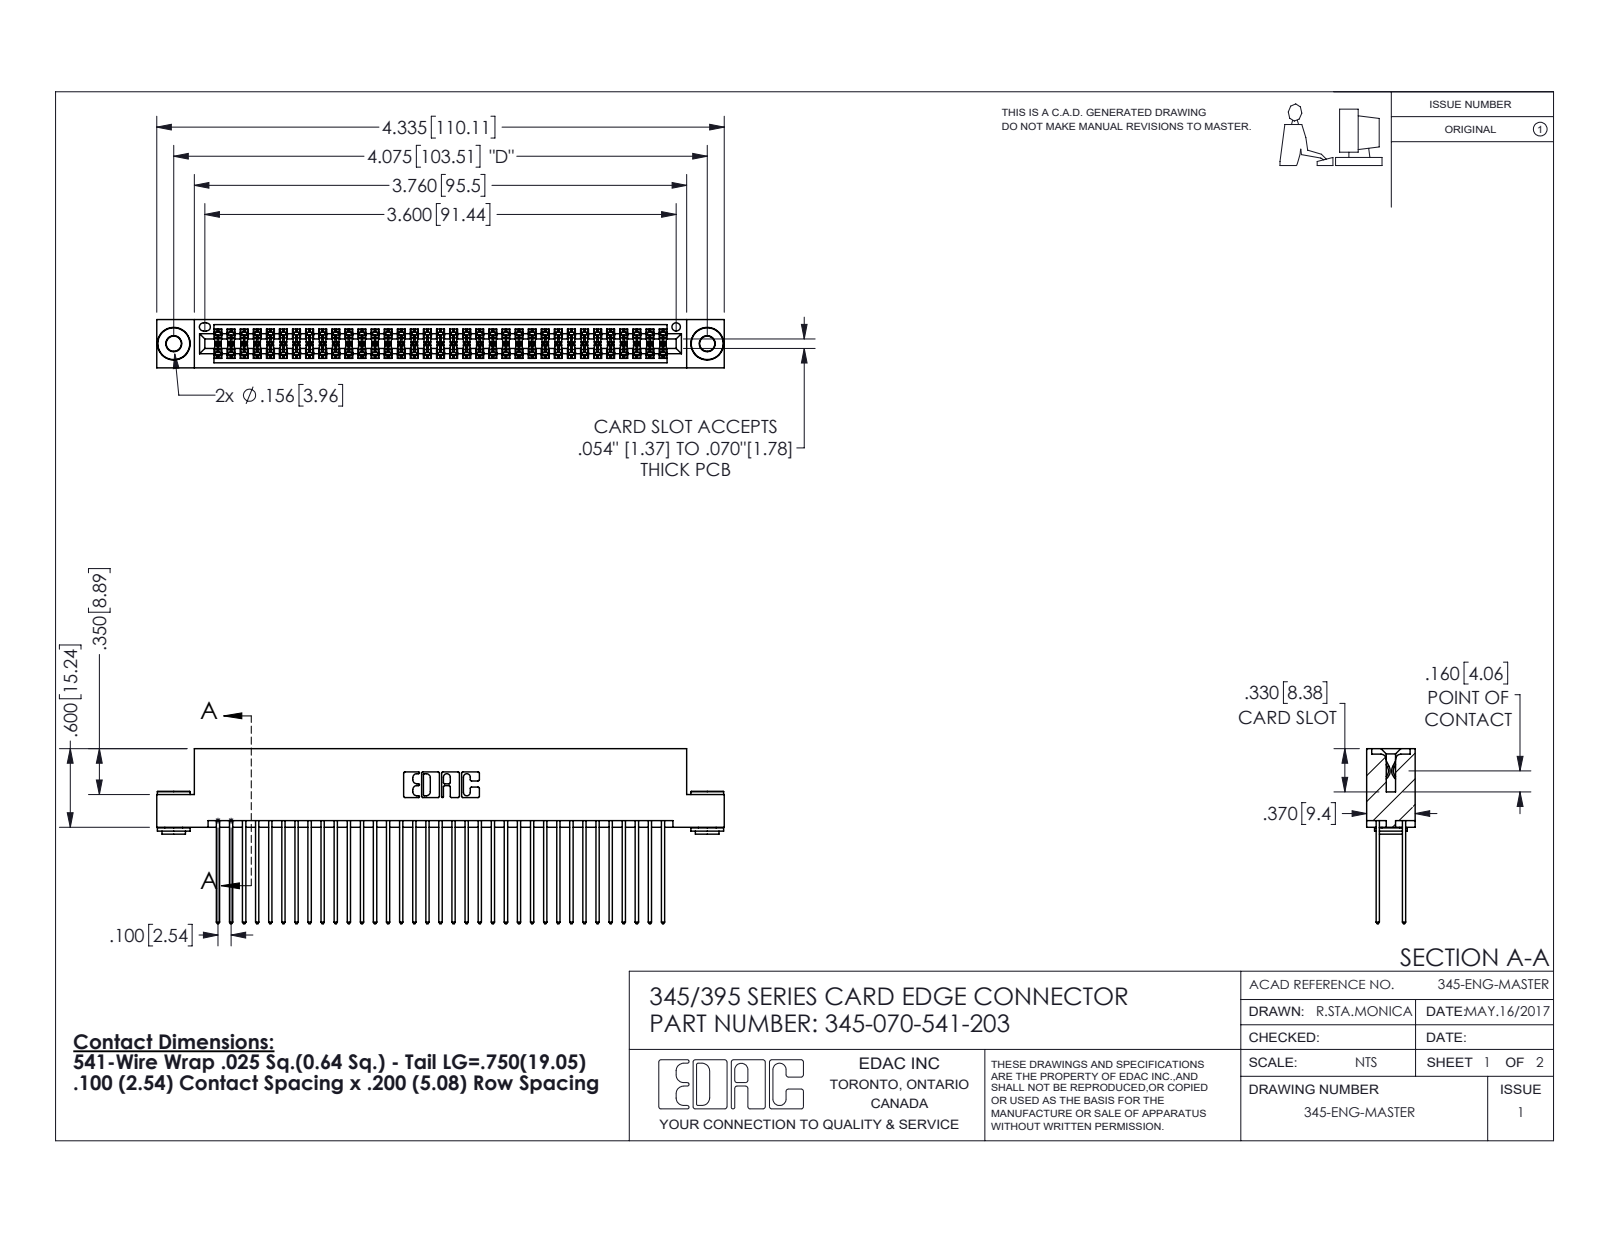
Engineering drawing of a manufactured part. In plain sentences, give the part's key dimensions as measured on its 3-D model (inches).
The part is named "345-070-541-203; 345 Part_Flush Mounting Lugs - 0.156 Dia-TH; 345-292-001_345-293-141; 345-250-002_345-250-002-102". Its 3-D file was written by "SolidWorks 2016 (CONFIG_CONTROL_DESIGN)". It is 73 solids with 3664 faces: 2400 planar, 1256 cylindrical and 8 other. Overall it measures 4.335 by 1.337 by 0.37 inches. Its volume is 0.674 cubic inches and its surface area 28.36 square inches. Round holes: 2 of diameter 0.116, 2 of diameter 0.156, 1 of diameter 0.064. Round bosses or shafts: 2 of diameter 0.25, 2 of diameter 0.18, 2 of diameter 0.136. Partial cylindrical surfaces (rounded edges, fillets, slot ends): 105 of radius 0.006, 70 of radius 0.01, 22 of radius 0.01, 6 of radius 0.007, 6 of radius 0.031, 3 of radius 0.026, 2 of radius 0.014, 2 of radius 0.019. The main face-to-face distances are 0.072, 0.298, 0.2, 0.025, 0.098, 0.272, 0.225, 0.37, 0.175, 0.149. The hole center spacings are 0.27, 3.839, 4.075.
